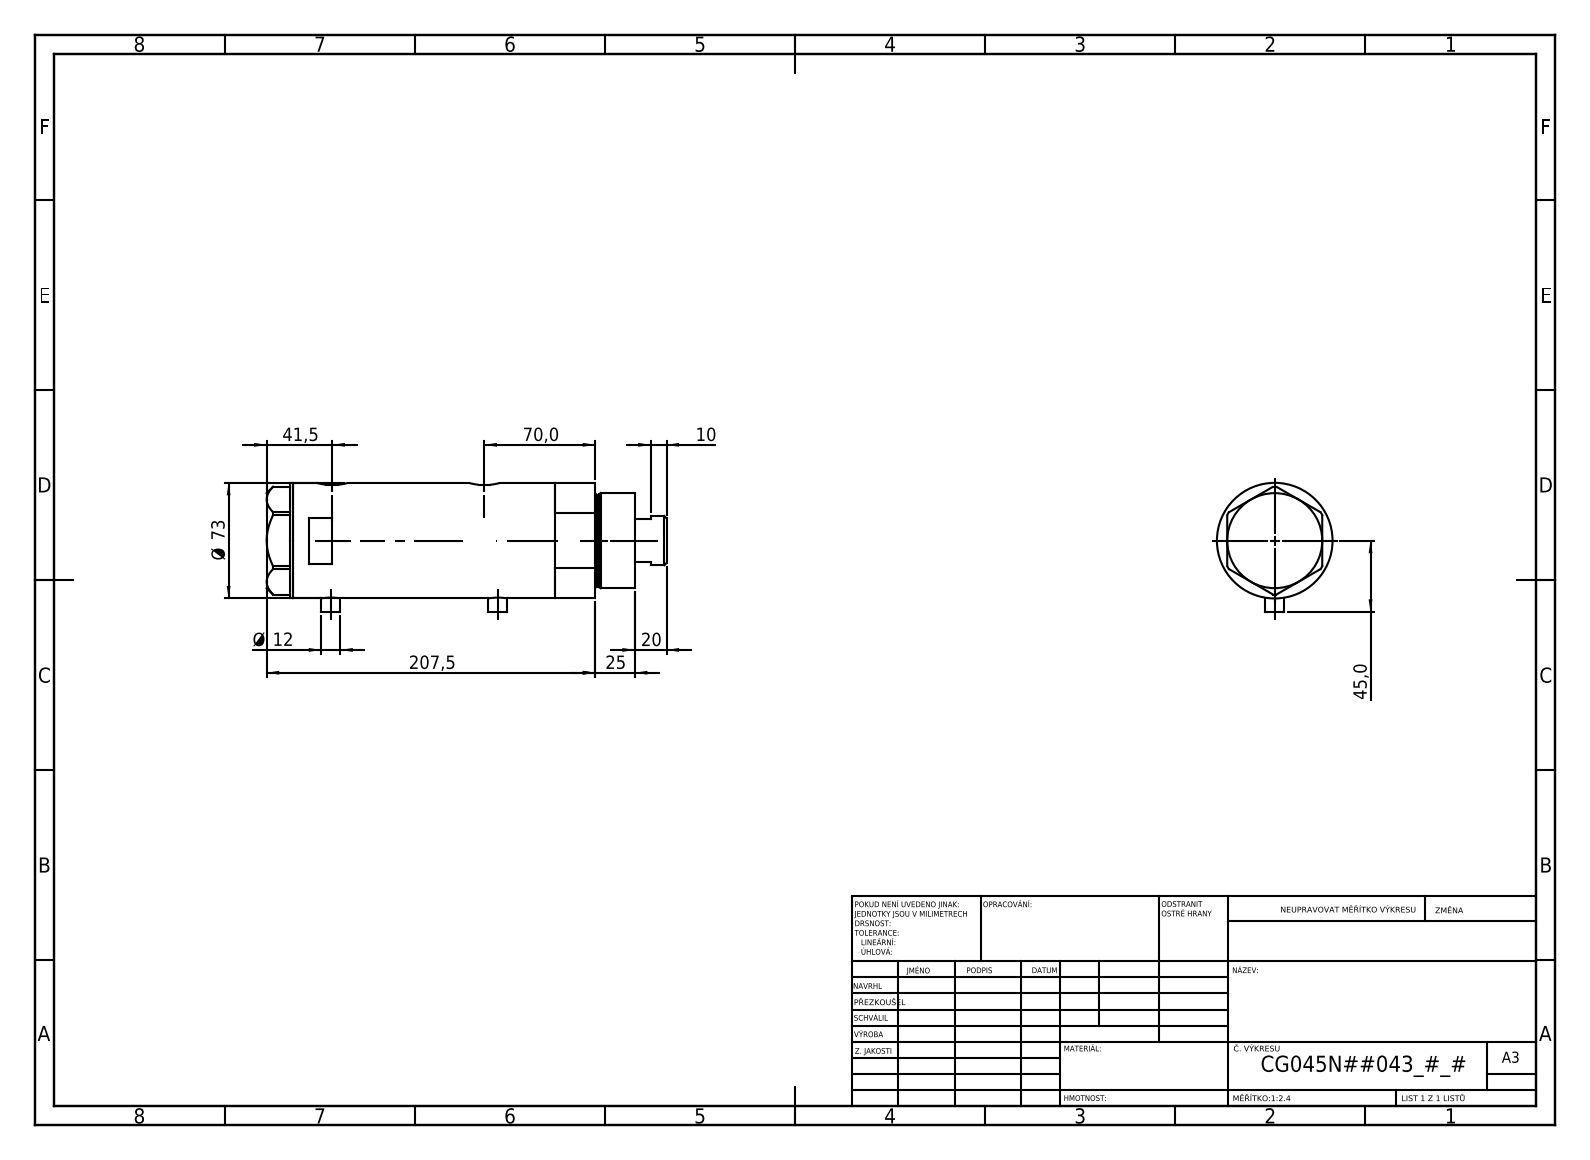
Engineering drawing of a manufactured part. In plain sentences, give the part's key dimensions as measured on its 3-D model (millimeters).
The part is named "V270CG_MIDDLE; V270CG_BACK; V270CG_FRONT; V270CG_VC". Its 3-D file was written by "SolidWorks 2019 (CONFIG_CONTROL_DESIGN)". It is 4 solids with 120 faces: 49 planar, 51 cylindrical and 20 other. Overall it measures 252.5 by 81.5 by 73 millimeters. Its volume is 891 648 cubic millimeters and its surface area 149 237 square millimeters. Round holes: 2 of diameter 12.5, 2 of diameter 13.16, 1 of diameter 10.5, 1 of diameter 32, 1 of diameter 33.5, 1 of diameter 45, 1 of diameter 48, 1 of diameter 64. Round bosses or shafts: 2 of diameter 12, 1 of diameter 73, 1 of diameter 60, 1 of diameter 58, 1 of diameter 31. Partial cylindrical surfaces (rounded edges, fillets, slot ends): 2 of radius 10. The main face-to-face distances are 95, 121, 26, 16.5, 42.5, 137.5, 2, 216, 232.5, 190. The hole center spacings are 1, 8.5, 96, 97, 104.5, 105.5.
